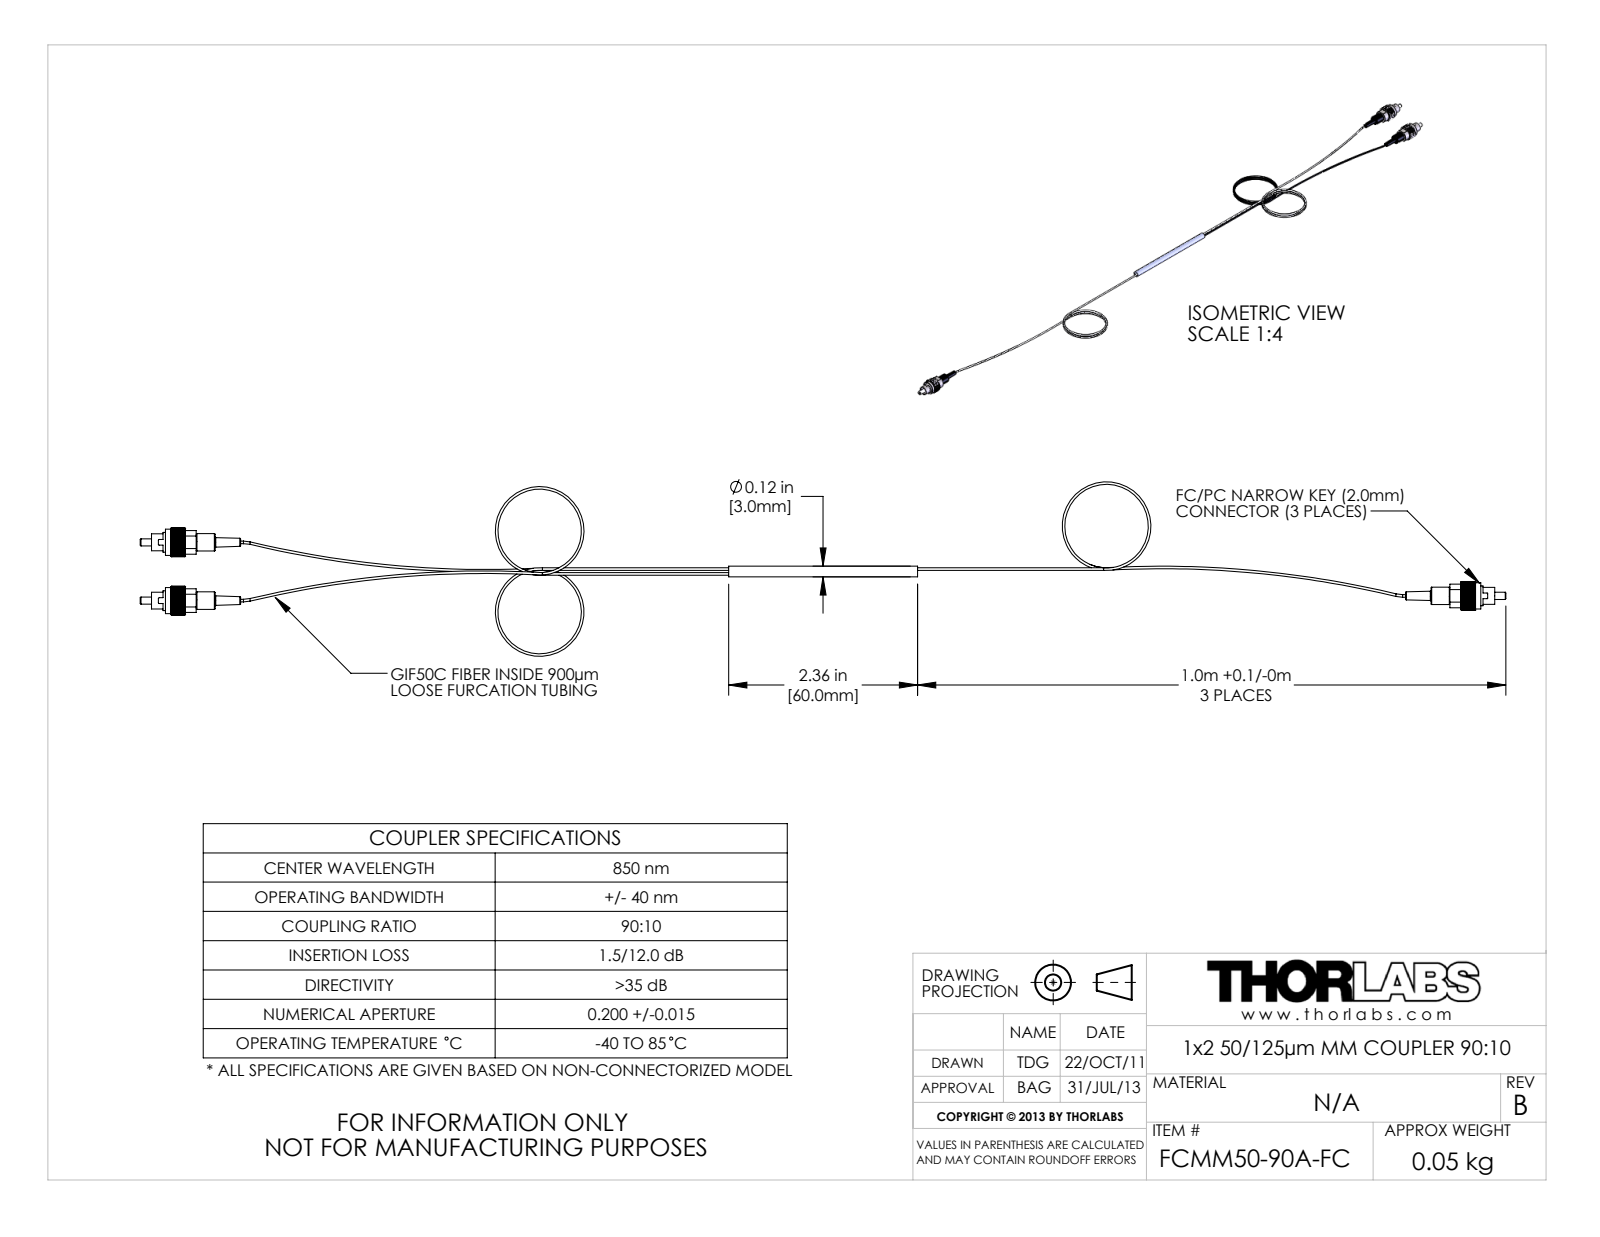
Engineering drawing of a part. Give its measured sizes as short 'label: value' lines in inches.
name: 13898-E0W
written by: SolidWorks 2012 (CONFIG_CONTROL_DESIGN)
unit: in
bodies: 13 solids, 904 faces (460 planar, 348 cylindrical, 96 other)
size: 18.778 × 2.4 × 0.63
volume: 0.228 in³; area: 16.9 in²
holes: 3× ⌀0.056, 3× ⌀0.192, 3× ⌀0.21, 3× ⌀0.25, 3× ⌀0.27, 3× ⌀0.325, 3× ⌀0.36, 2× ⌀0.039, 1× ⌀0.13
bosses: 5× ⌀0.035, 3× ⌀0.272, 3× ⌀0.24, 3× ⌀0.232, 3× ⌀0.19, 3× ⌀0.157, 3× ⌀0.141, 3× ⌀0.098
rounds: 6× R0.01, 3× R0.163, 3× R0.197
face distances: 0.267, 0.267, 0.263, 0.116, 0.147, 0.031, 0.513, 0.397, 0.25, 17.648
hole spacings: 0.386, 0.033, 0.417, 0.449, 0.065, 0.245, 0.325, 0.355
